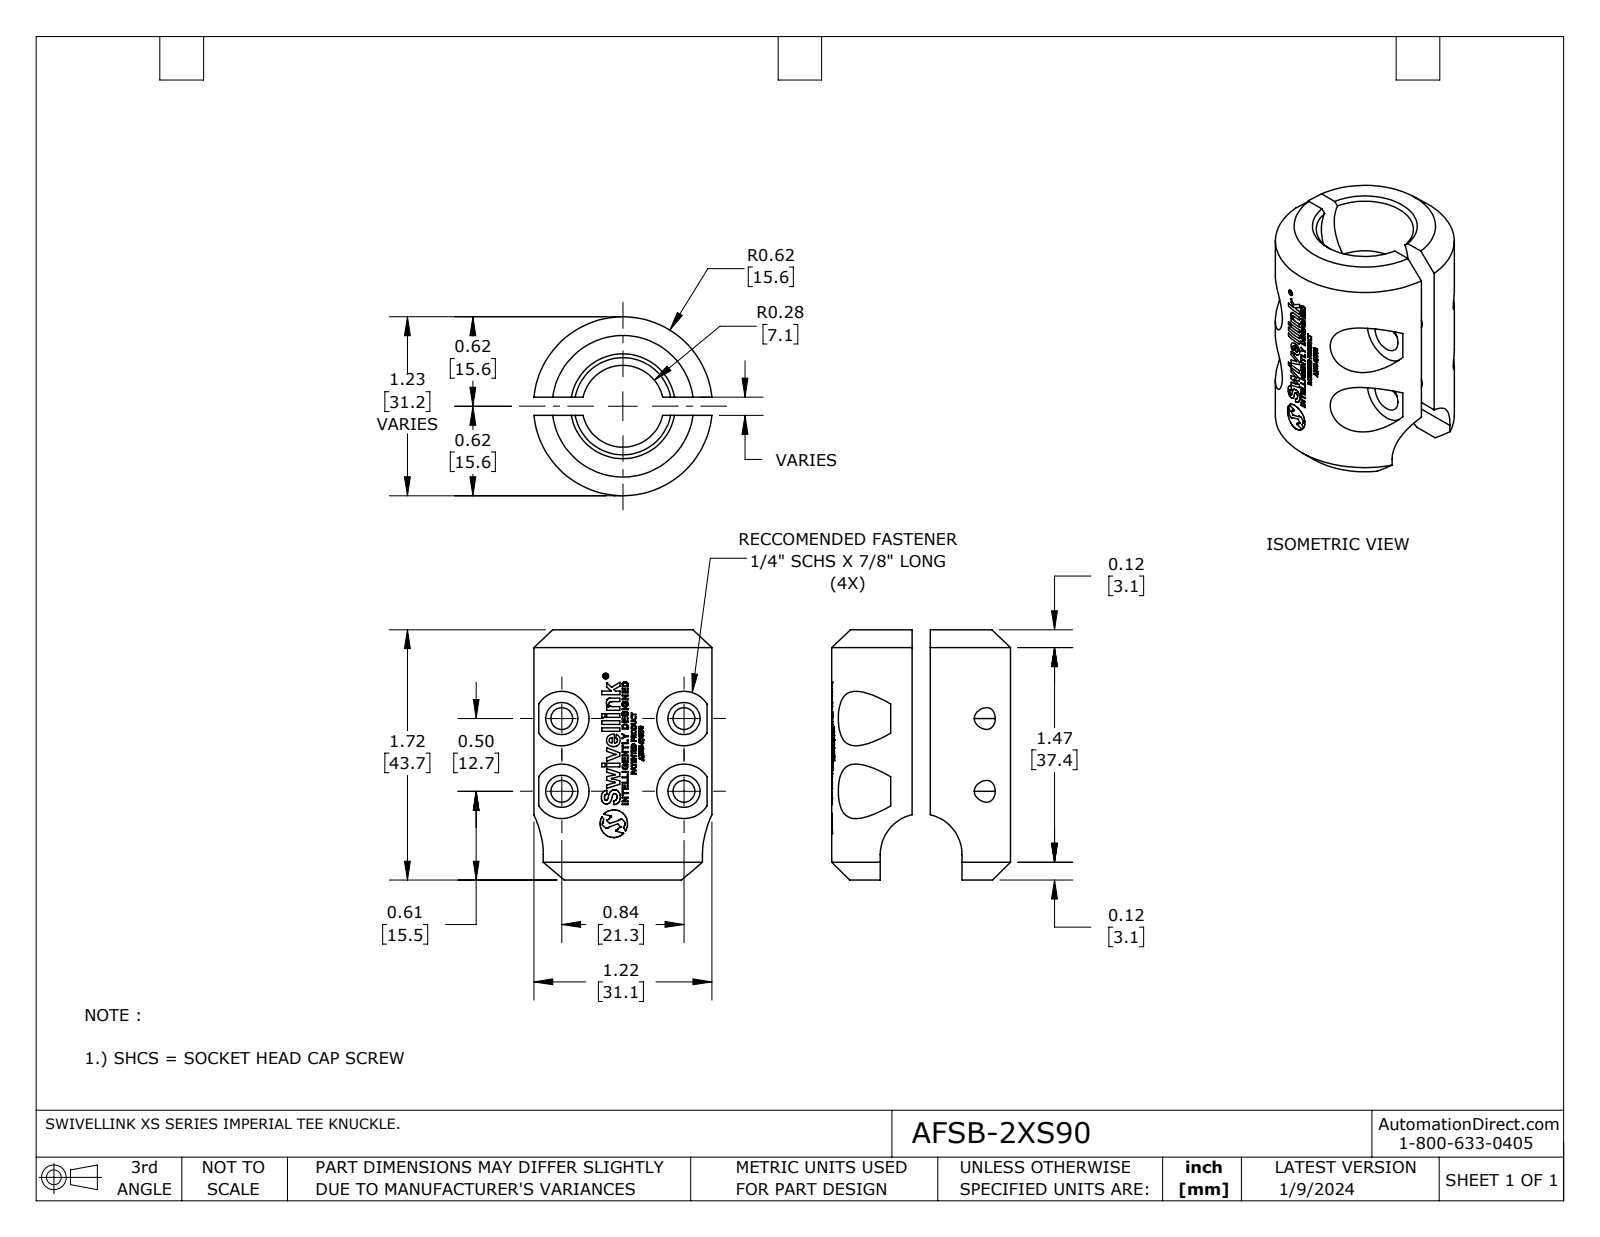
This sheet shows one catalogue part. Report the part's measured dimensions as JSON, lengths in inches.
{"part_name": "AFSB-2XS90", "step_written_by": "SolidWorks 2023 (AUTOMOTIVE_DESIGN)", "units": "inches", "bodies": {"solids": 2, "faces": 136, "planar": 16, "cylindrical": 108, "other": 12}, "overall_size": [1.72, 1.23, 1.224], "volume_in3": 1.094, "surface_area_in2": 12.88, "round_holes": [[0.15, 4], [0.221, 4], [0.375, 4], [0.562, 1]], "round_bosses_or_shafts": [[1.23, 1]], "partial_cylinders_radius": [[0.281, 1]], "face_to_face_distances": [0.125, 0.272, 0.146, 0.219, 0.344, 1.72, 0.072, 0.49, 0.562], "hole_center_spacings": [0.5, 0.84, 0.978]}
